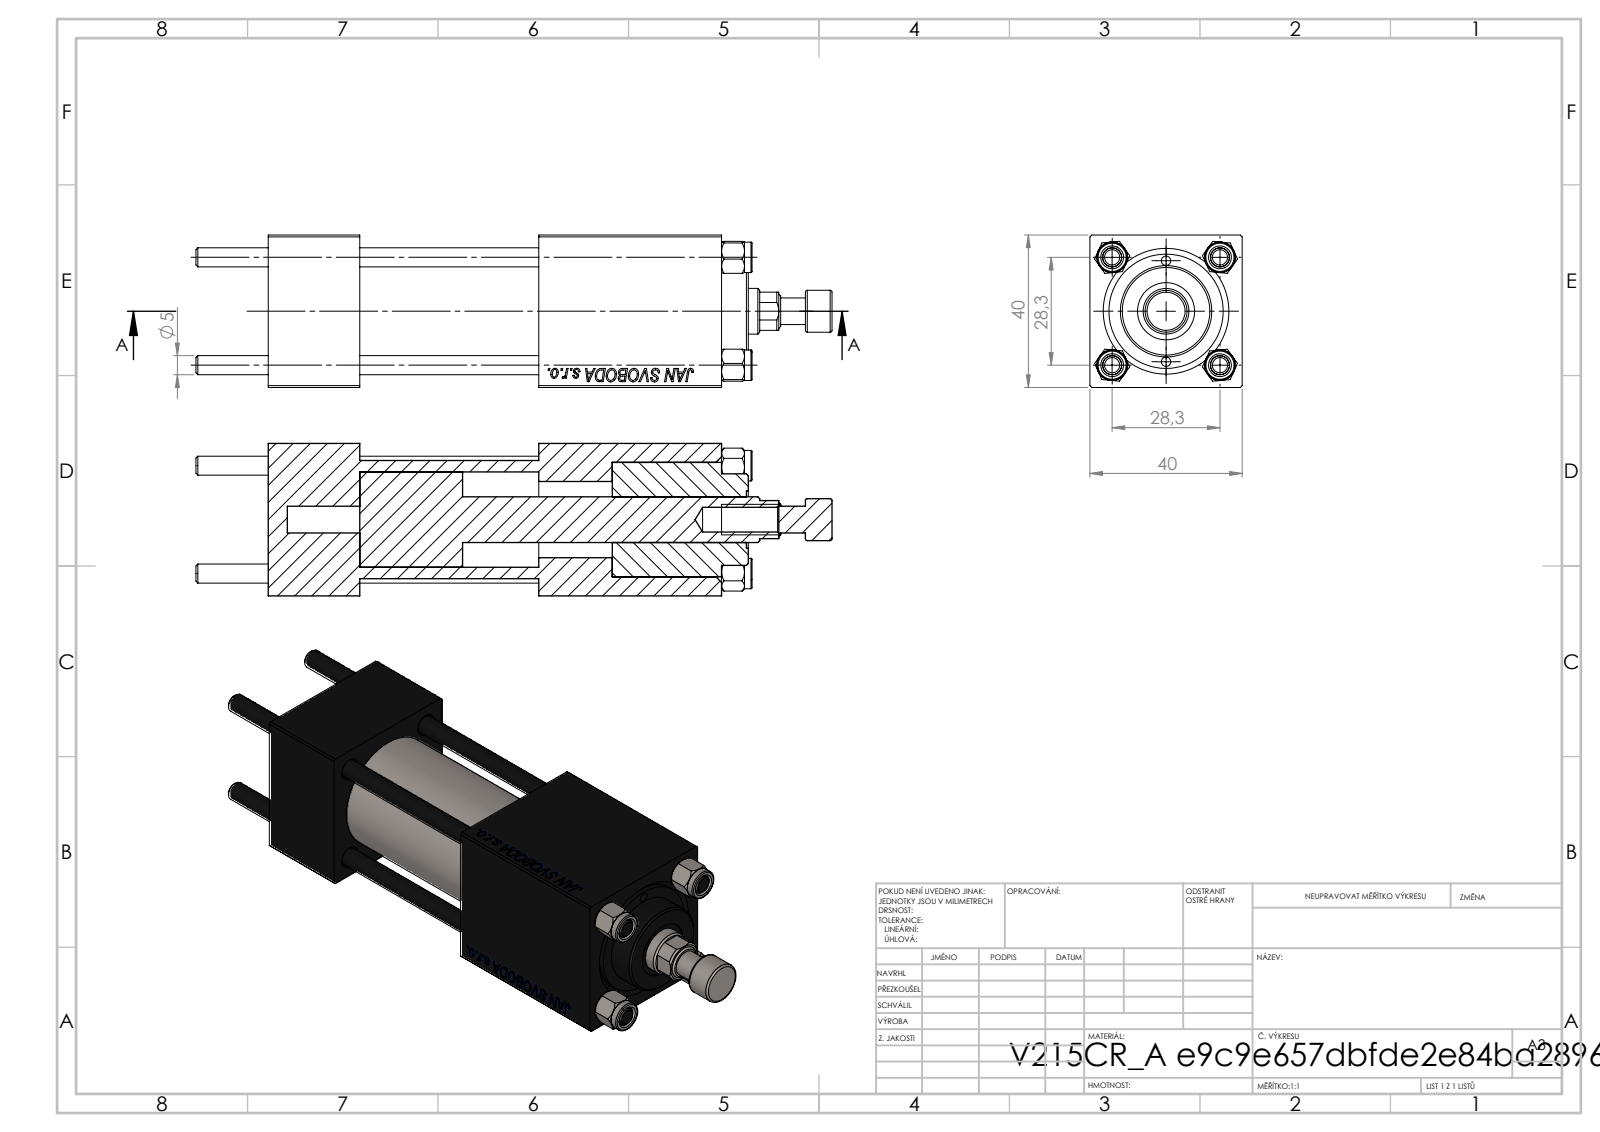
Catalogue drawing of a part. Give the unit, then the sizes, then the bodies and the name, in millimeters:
Units: millimetres
Overall size (bounding box): 167 × 40 × 40
Round holes (diameter × count): ⌀5 ×4, ⌀20 ×3, ⌀2.5 ×2, ⌀7 ×2, ⌀13.16 ×2, ⌀6.5 ×1, ⌀12 ×1, ⌀15 ×1, ⌀25 ×1, ⌀30 ×1
Round bosses / shafts (diameter × count): ⌀8 ×4, ⌀31 ×1, ⌀24 ×1, ⌀11 ×1
Main face-to-face distances: 40, 24, 90.3, 66.3, 119, 95, 28.7, 71, 47, 19.3
Hole centre spacings: 14.18, 20.01, 28.3, 30.84, 13.25, 40.02, 26.5, 72
Volume: 145 715 mm³ · Surface area: 59 566 mm²
Bodies: 12 solids, 1151 faces (523 planar, 86 cylindrical, 542 other)
Part name (STEP PRODUCT): V215_VC_A; CR025_012_A_0_G_A_G_M_020_+#_##_TYCINKA; V215CR_BODY_A; V215CR_VCP (+2 more)
STEP written by: SolidWorks 2019 (CONFIG_CONTROL_DESIGN)
